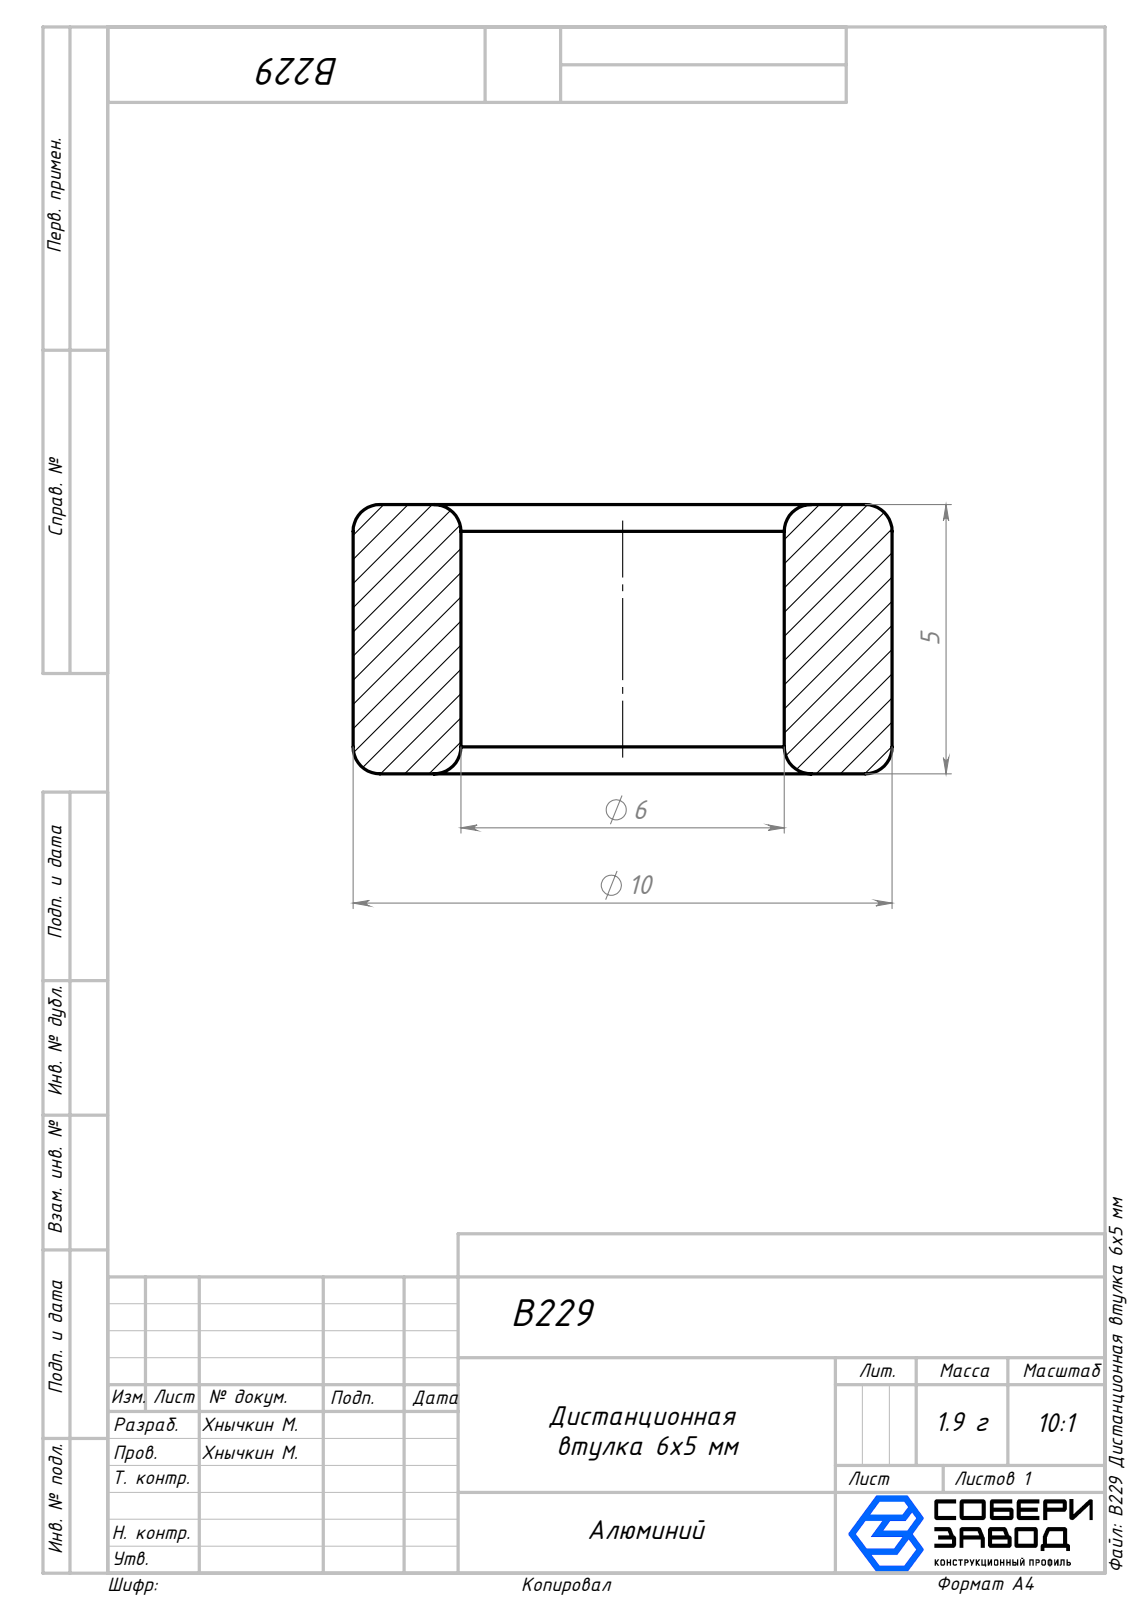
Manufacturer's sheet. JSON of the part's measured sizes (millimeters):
{"part_name": "B229 Дистанционная втулка 6x5 мм", "step_written_by": "SolidWorks 2026 (AUTOMOTIVE_DESIGN)", "units": "millimeters", "bodies": {"solids": 1, "faces": 14, "planar": 2, "cylindrical": 4, "other": 8}, "overall_size": [10, 10, 5], "volume_mm3": 246, "surface_area_mm2": 330, "round_holes": [[6, 1]], "round_bosses_or_shafts": [[10, 1]], "face_to_face_distances": [5]}
